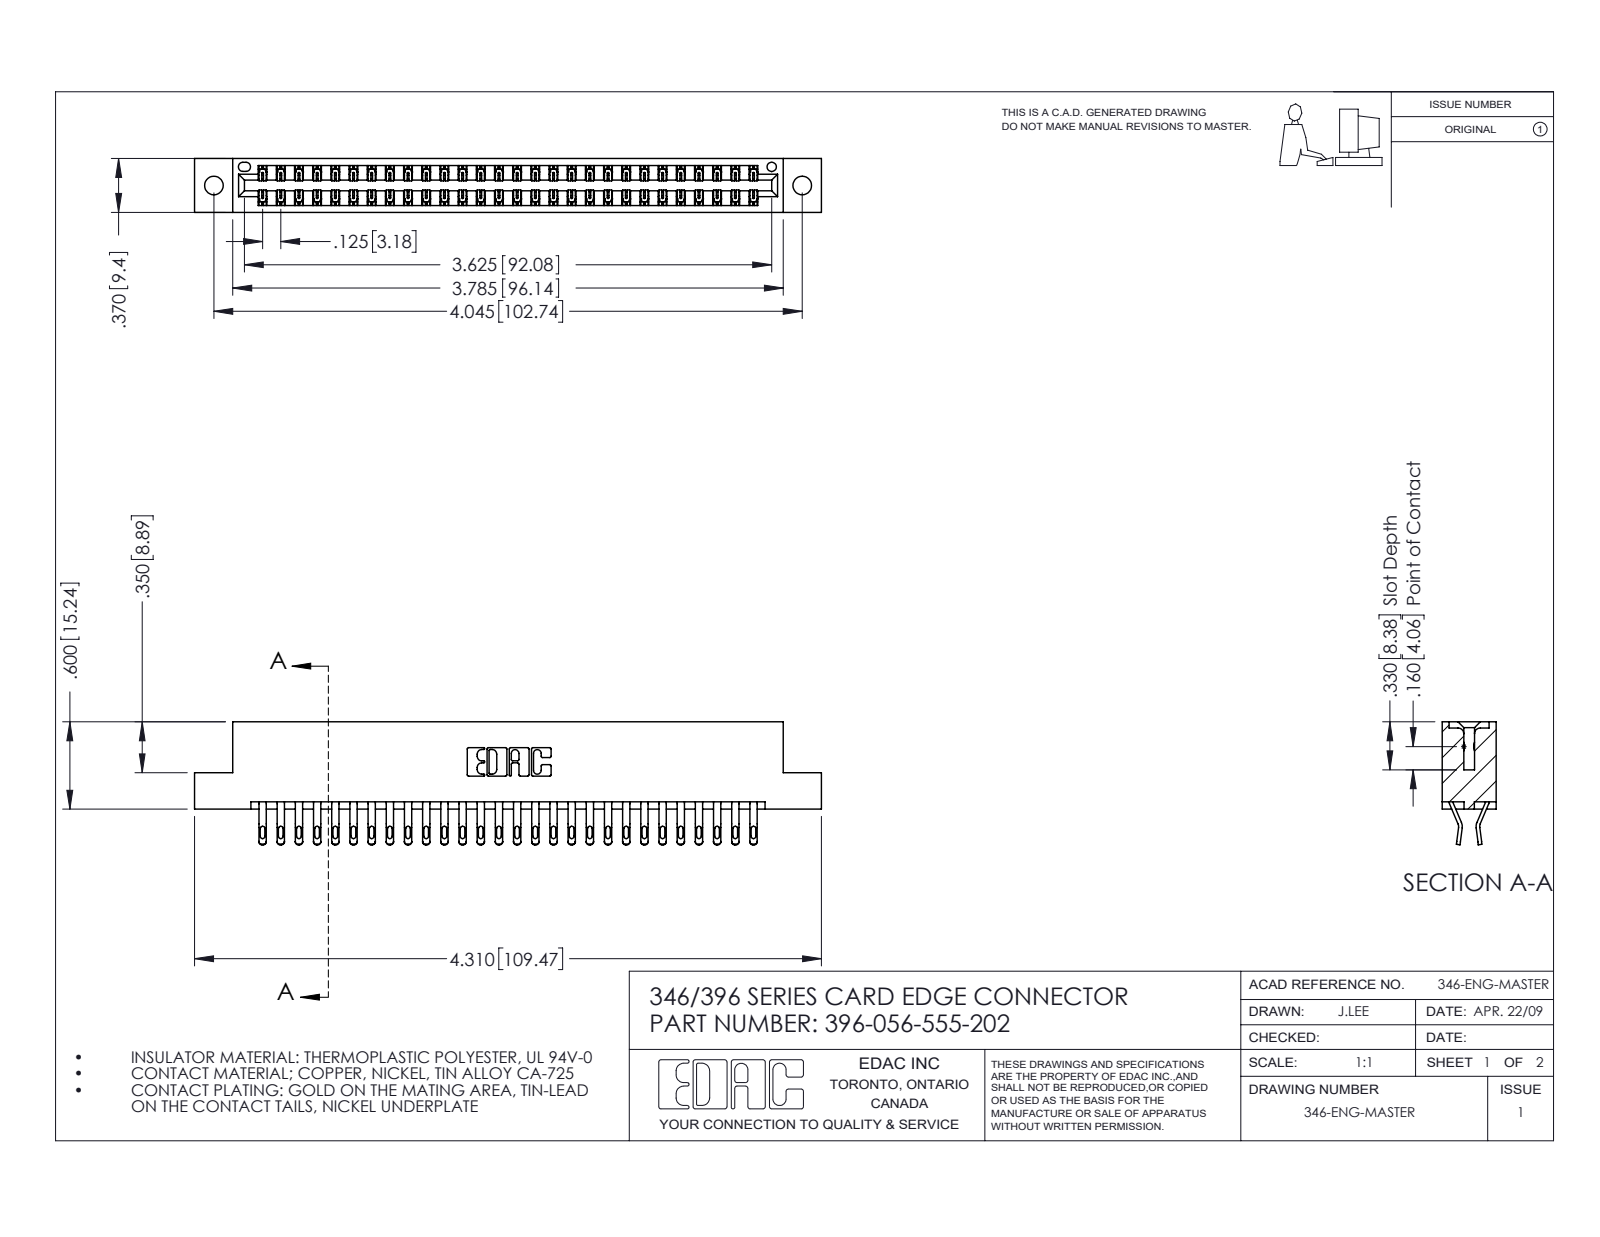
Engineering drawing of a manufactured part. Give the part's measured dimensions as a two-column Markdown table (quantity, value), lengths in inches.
| quantity | value |
| --- | --- |
| part name | 396-056-555-202; 345-292-001_555 Tail; 346 Part_Flush Mounting Lugs - 0.128 Dia |
| STEP written by | SolidWorks 2016 (CONFIG_CONTROL_DESIGN) |
| units | inches |
| bodies | 57 solids, 3370 faces (1924 planar, 1446 cylindrical, 0 other) |
| overall size | 4.31 × 0.845 × 0.37 |
| volume | 0.652 in³ |
| surface area | 22.92 in² |
| round holes (diameter × count) | 0.128 × 2, 0.064 × 1 |
| partial cylindrical surfaces (radius × count) | 0.016 × 112, 0.02 × 112, 0.006 × 84, 0.01 × 22, 0.007 × 6, 0.031 × 6, 0.026 × 3, 0.01 × 2 |
| main face-to-face distances | 0.048, 0.322, 0.37, 0.25, 0.025, 0.072, 0.298, 0.275, 0.148, 0.222 |
| hole center spacings | 0.246, 3.837, 4.045 |
